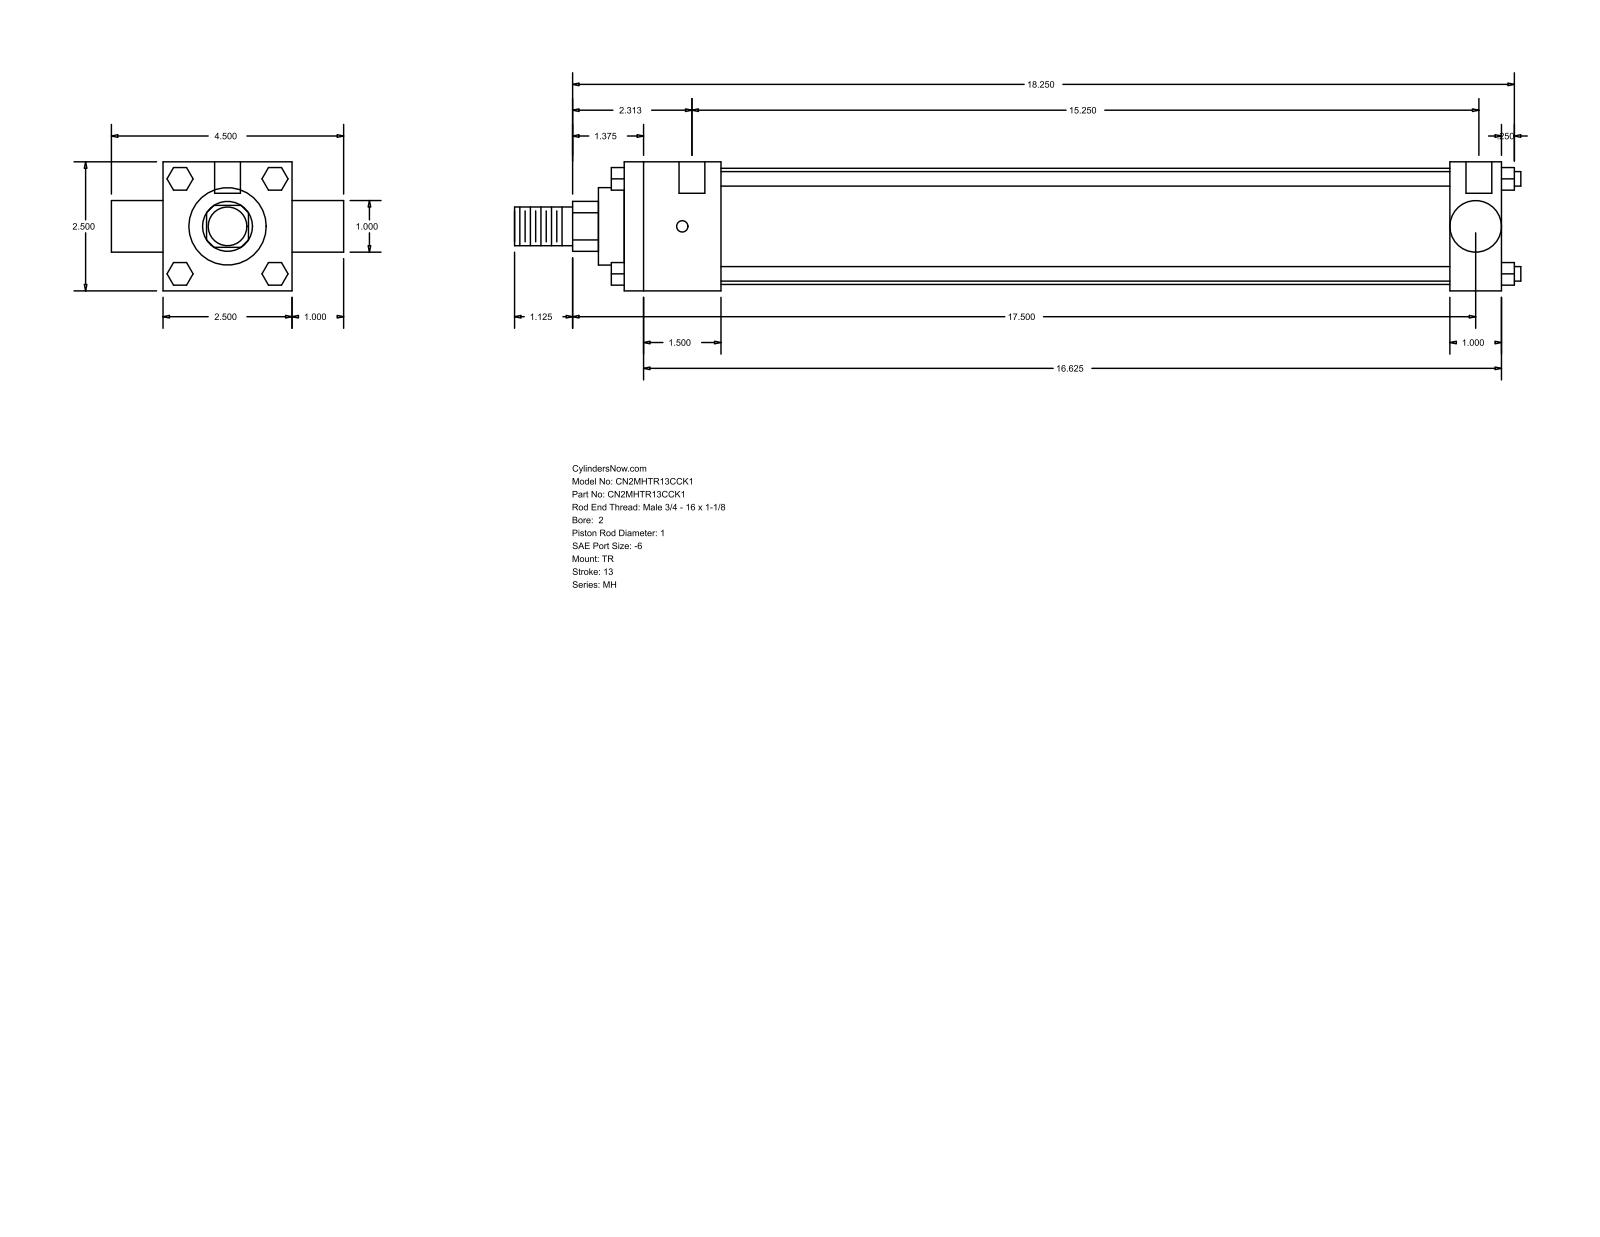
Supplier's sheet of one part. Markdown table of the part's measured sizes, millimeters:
| quantity | value |
| --- | --- |
| part name | MH_TR__0200_1 |
| STEP written by | GSSL Pune (CONFIG_CONTROL_DESIGN) |
| units | millimeters |
| bodies | 0 solids, 120 faces (92 planar, 28 cylindrical, 0 other) |
| overall size | 495.3 × 114.3 × 63.5 |
| round holes (diameter × count) | 5.56 × 3, 12.7 × 2 |
| round bosses / shafts (diameter × count) | 7.14 × 4, 57.15 × 1, 38.1 × 1, 25.4 × 1, 25.35 × 1, 19.05 × 1 |
| partial cylindrical surfaces (radius × count) | 12.29 × 1 |
| main face-to-face distances | 63.5, 431.8, 25.4, 47.63, 406.4, 358.77, 384.17, 88.9, 444.5, 6.35 |
| hole center spacings | 3.17, 4.76, 387.35, 390.52, 392.11, 395.28 |
